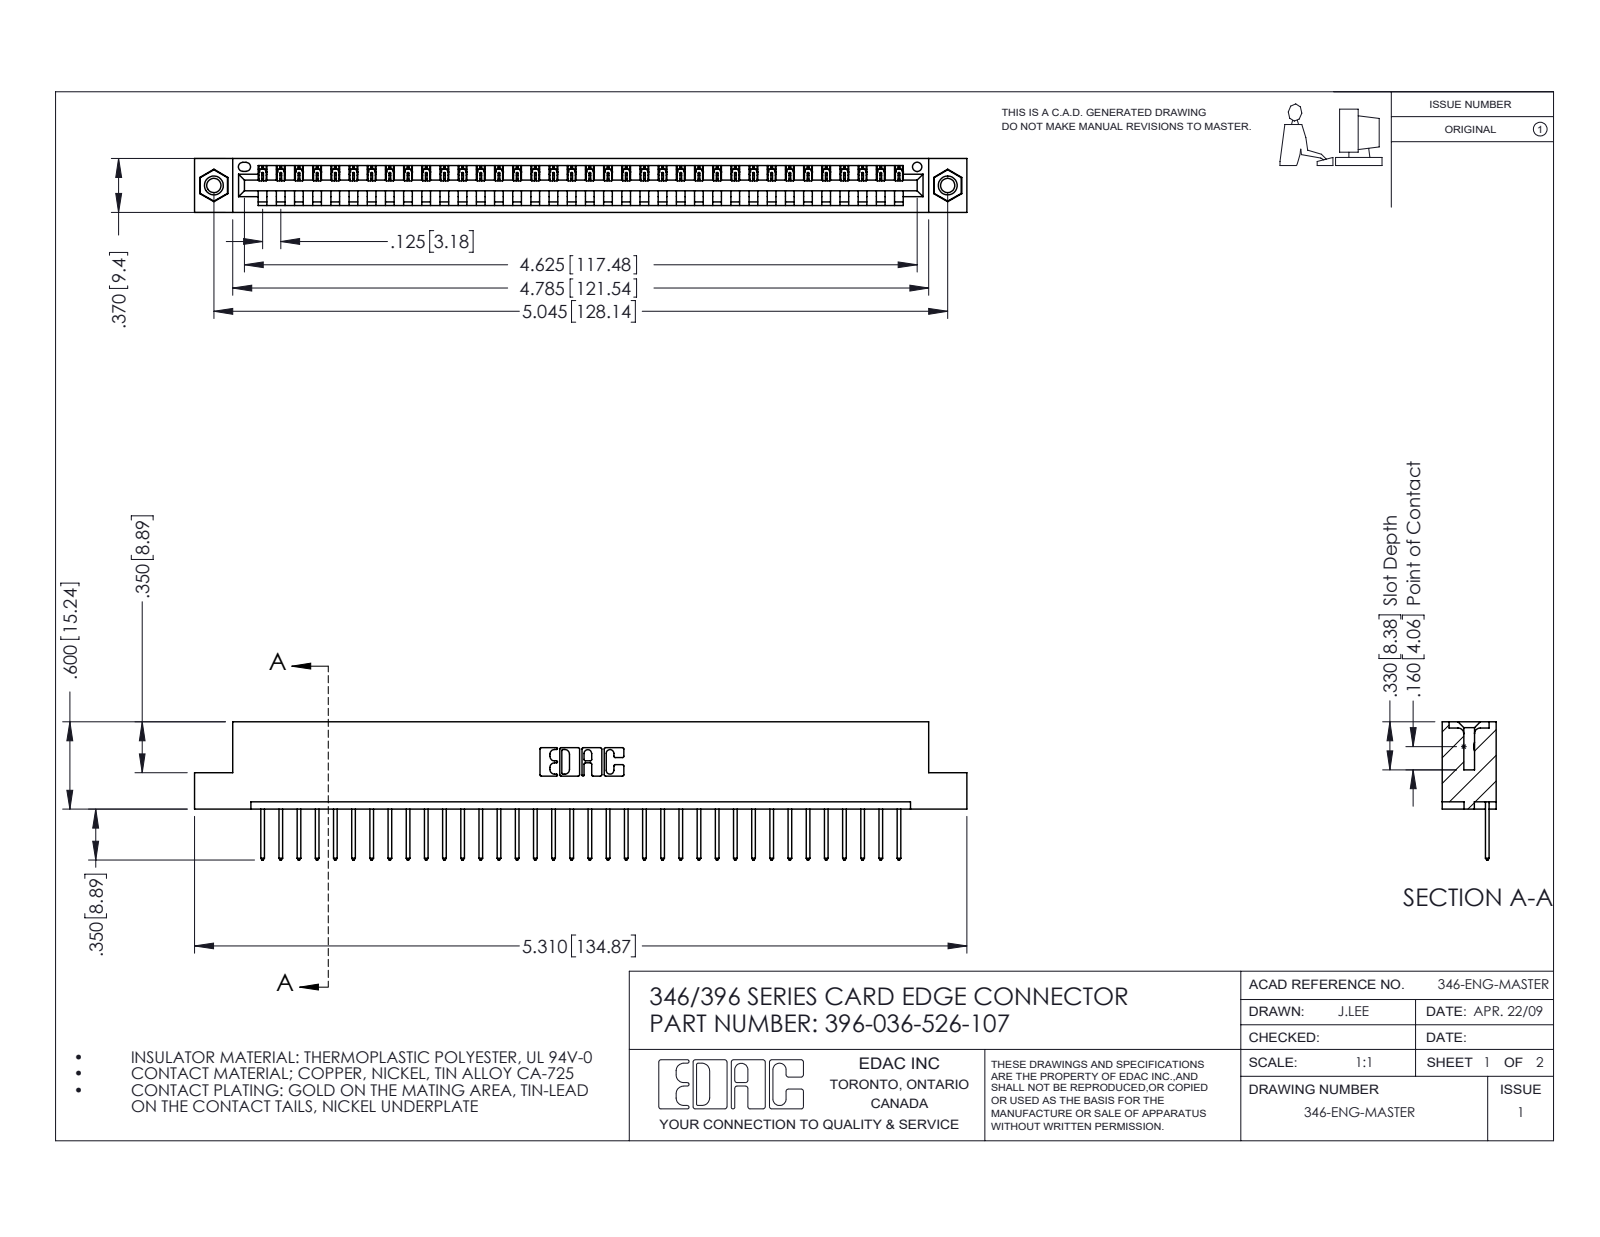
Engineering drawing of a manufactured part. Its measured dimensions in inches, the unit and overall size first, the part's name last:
Units: inches
Overall size (bounding box): 5.31 × 0.95 × 0.37
Round holes (diameter × count): ⌀0.098 ×2, ⌀0.125 ×2, ⌀0.156 ×2, ⌀0.064 ×1
Round bosses / shafts (diameter × count): ⌀0.155 ×2
Partial cylindrical surfaces — rounded edges, fillets, slot ends (radius × count): R0.006 ×72, R0.01 ×72, R0.01 ×22, R0.007 ×6, R0.031 ×6, R0.026 ×3, R0.031 ×2, R0.04 ×2
Main face-to-face distances: 0.048, 0.322, 0.37, 0.25, 0.072, 0.298, 0.025, 0.148, 0.222, 0.1
Hole centre spacings: 0.246, 4.836, 5.045
Volume: 0.783 in³ · Surface area: 24.75 in²
Bodies: 39 solids, 2270 faces (1548 planar, 706 cylindrical, 16 other)
Part name (STEP PRODUCT): 346 Part_Flush Mounting Lugs - 0.156 Dia-TI; 345-292-001_345-293-126; 345-250-001_345-250-005-103; 396-036-526-107
STEP written by: SolidWorks 2016 (CONFIG_CONTROL_DESIGN)
